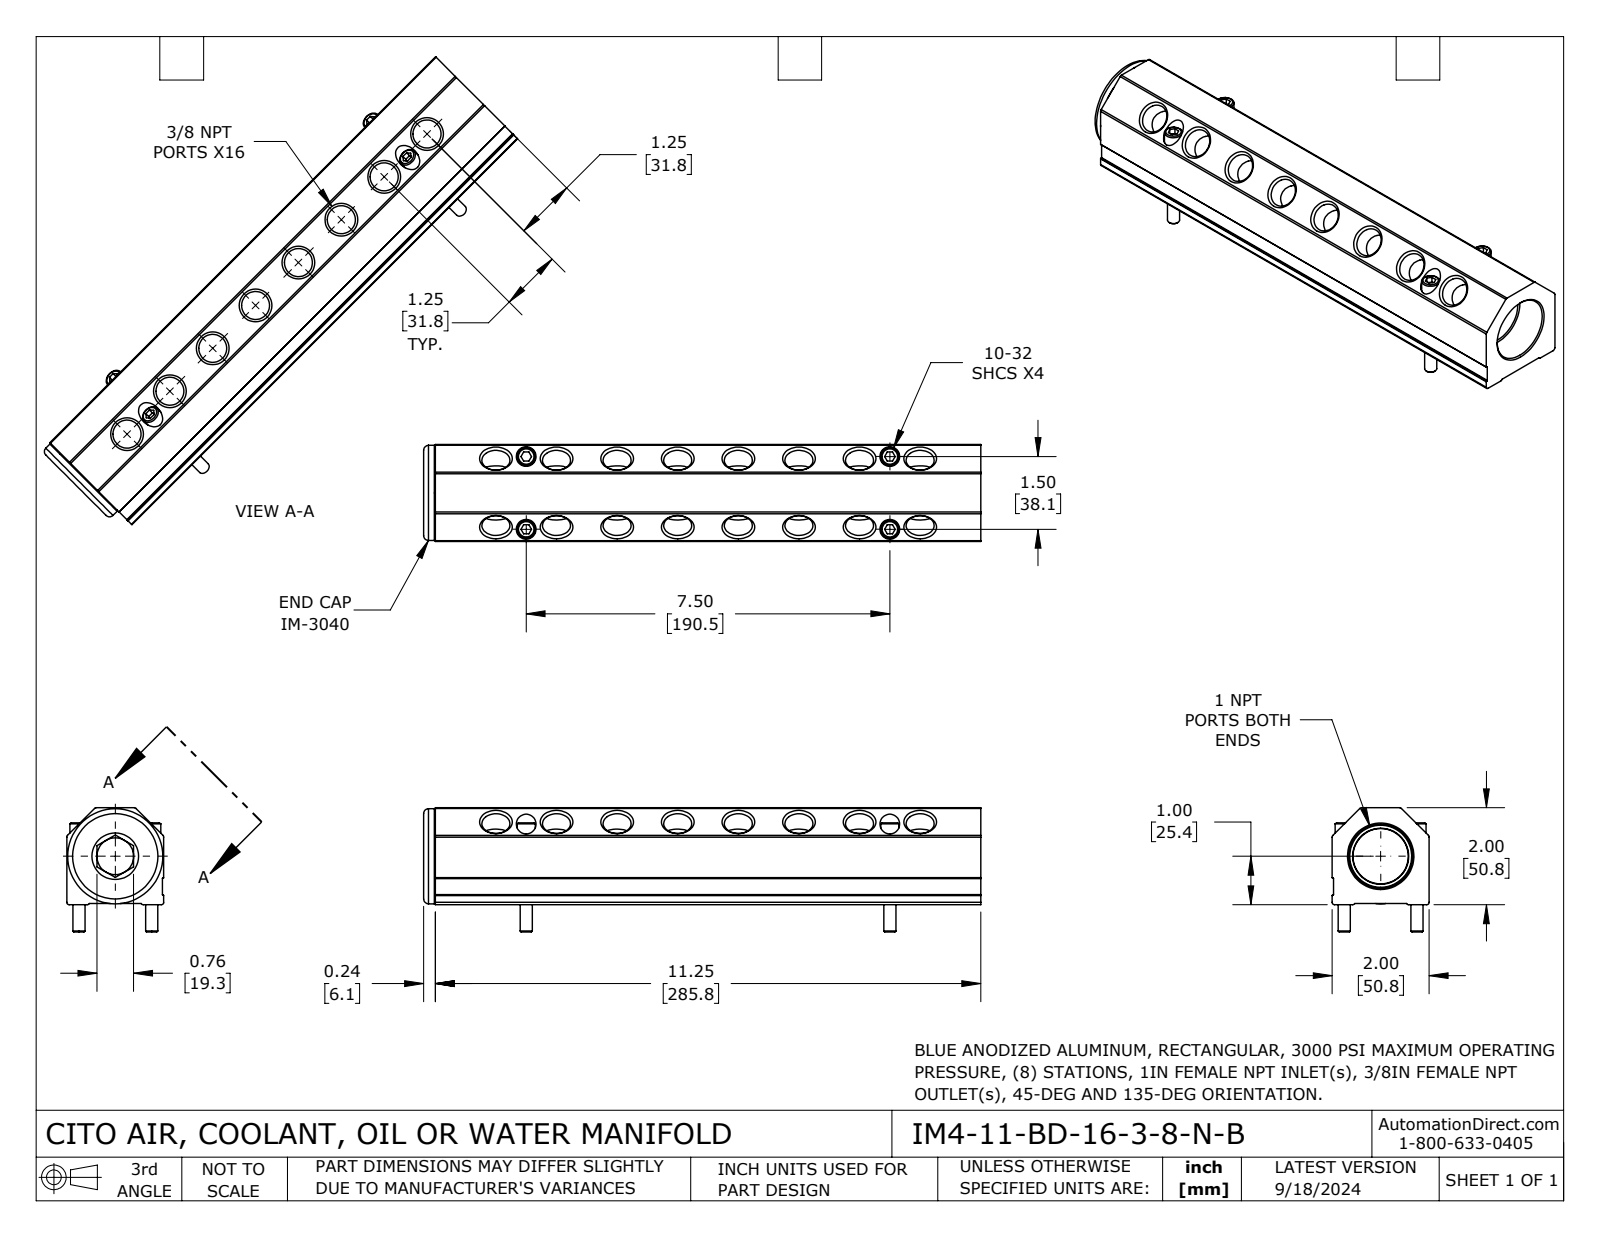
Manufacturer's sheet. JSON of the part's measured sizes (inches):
{"part_name": "IM4-11-BD-16-3-8-N-B", "step_written_by": "SolidWorks 2023 (CONFIG_CONTROL_DESIGN)", "units": "inches", "bodies": {"solids": 6, "faces": 245, "planar": 81, "cylindrical": 90, "other": 74}, "overall_size": [11.49, 2.56, 2], "volume_in3": 27.69, "surface_area_in2": 158.4, "round_holes": [[0.578, 16], [0.266, 4], [0.406, 4], [0.758, 1], [1.156, 1], [1.637, 1]], "round_bosses_or_shafts": [[0.375, 4], [0.25, 4], [1.96, 1], [1.359, 1], [1.293, 1], [1.14, 1]], "partial_cylinders_radius": [[0.05, 8], [0.01, 4]], "face_to_face_distances": [2, 1.975, 0.025, 0.028, 1.972, 11.25, 0.24, 11.49, 0.764, 0.524], "hole_center_spacings": [1.25, 2.5, 3.75, 5, 6.25, 7.5, 1.5, 7.648]}
